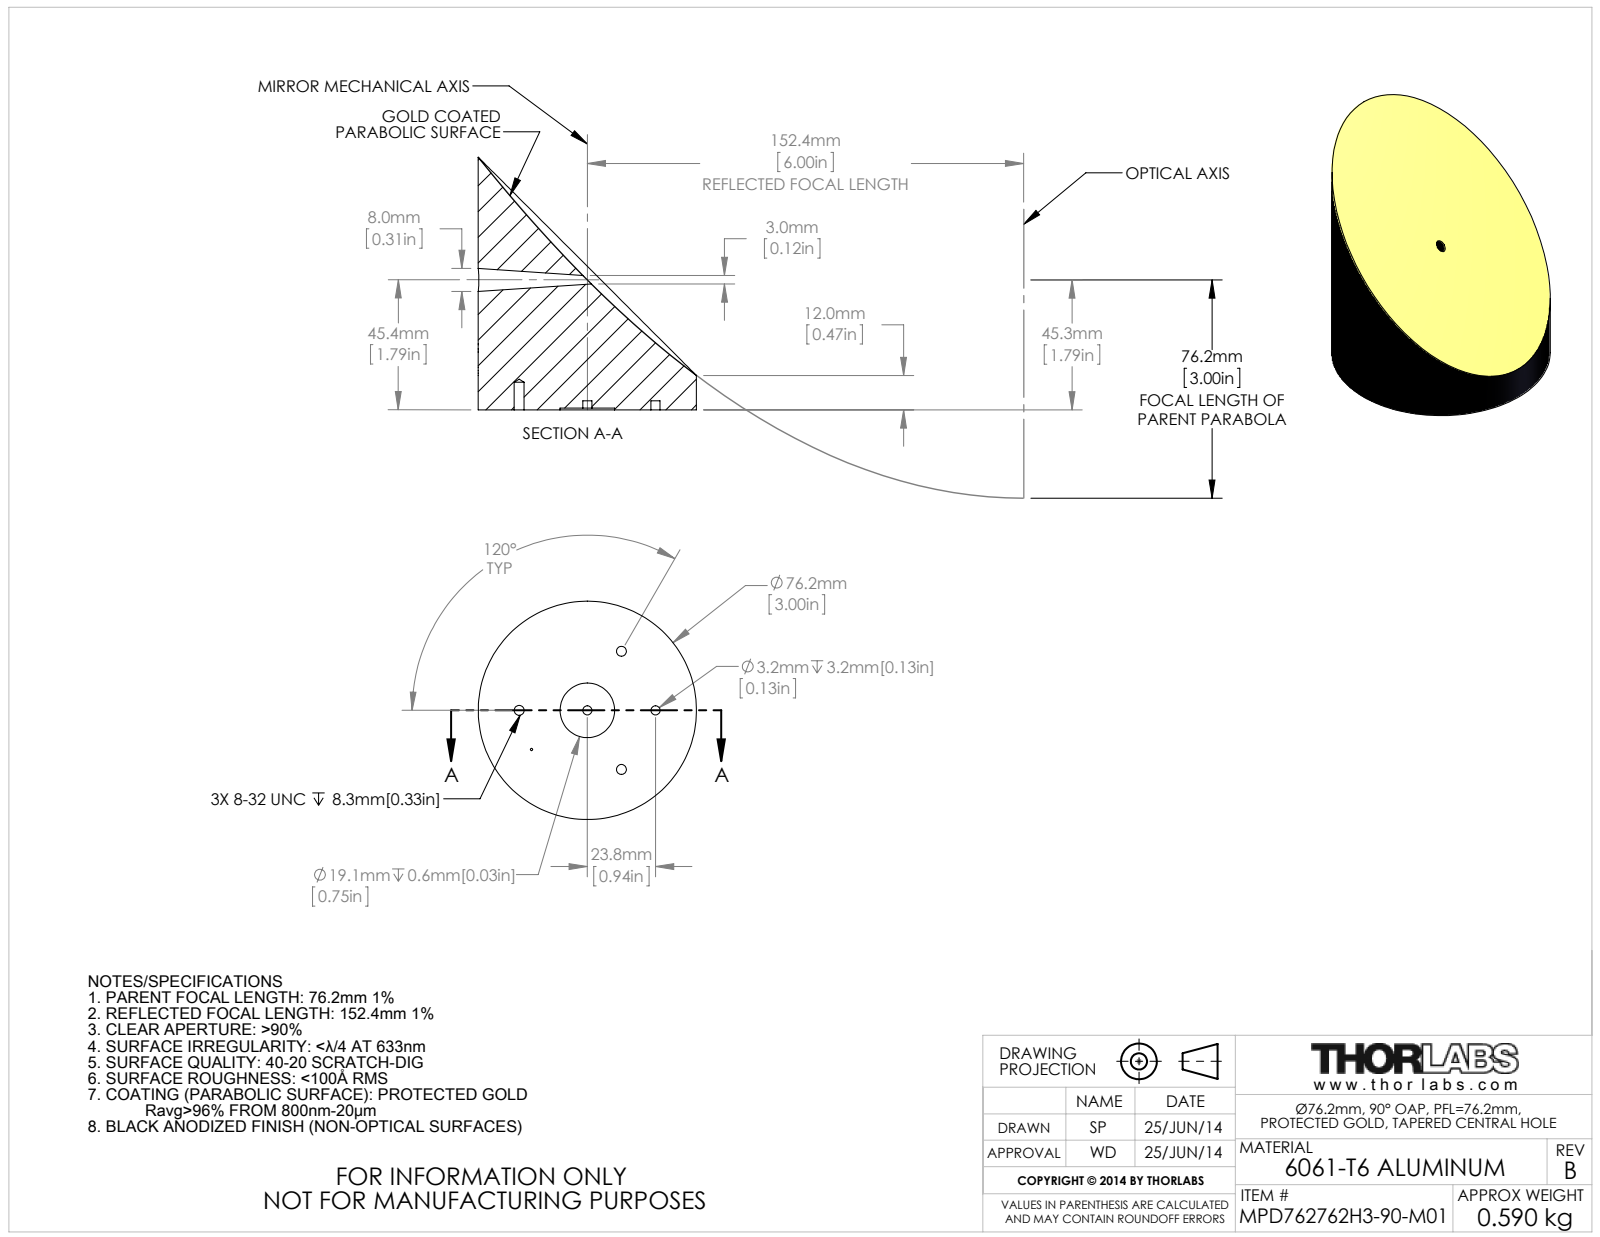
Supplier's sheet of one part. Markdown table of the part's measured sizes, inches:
| quantity | value |
| --- | --- |
| part name | 24803-E0W |
| STEP written by | SolidWorks 2014 (CONFIG_CONTROL_DESIGN) |
| units | inches |
| bodies | 1 solid, 68 faces (4 planar, 52 cylindrical, 12 other) |
| overall size | 3.473 × 3 × 3 |
| volume | 13.19 in³ |
| surface area | 37.28 in² |
| round holes (diameter × count) | 0.136 × 3, 0.126 × 2, 0.75 × 1 |
| round bosses / shafts (diameter × count) | 3 × 1 |
| main face-to-face distances | 0.025, 0.125, 0.1 |
| hole center spacings | 0.937, 0.938, 1.624, 1.624, 1.875 |
